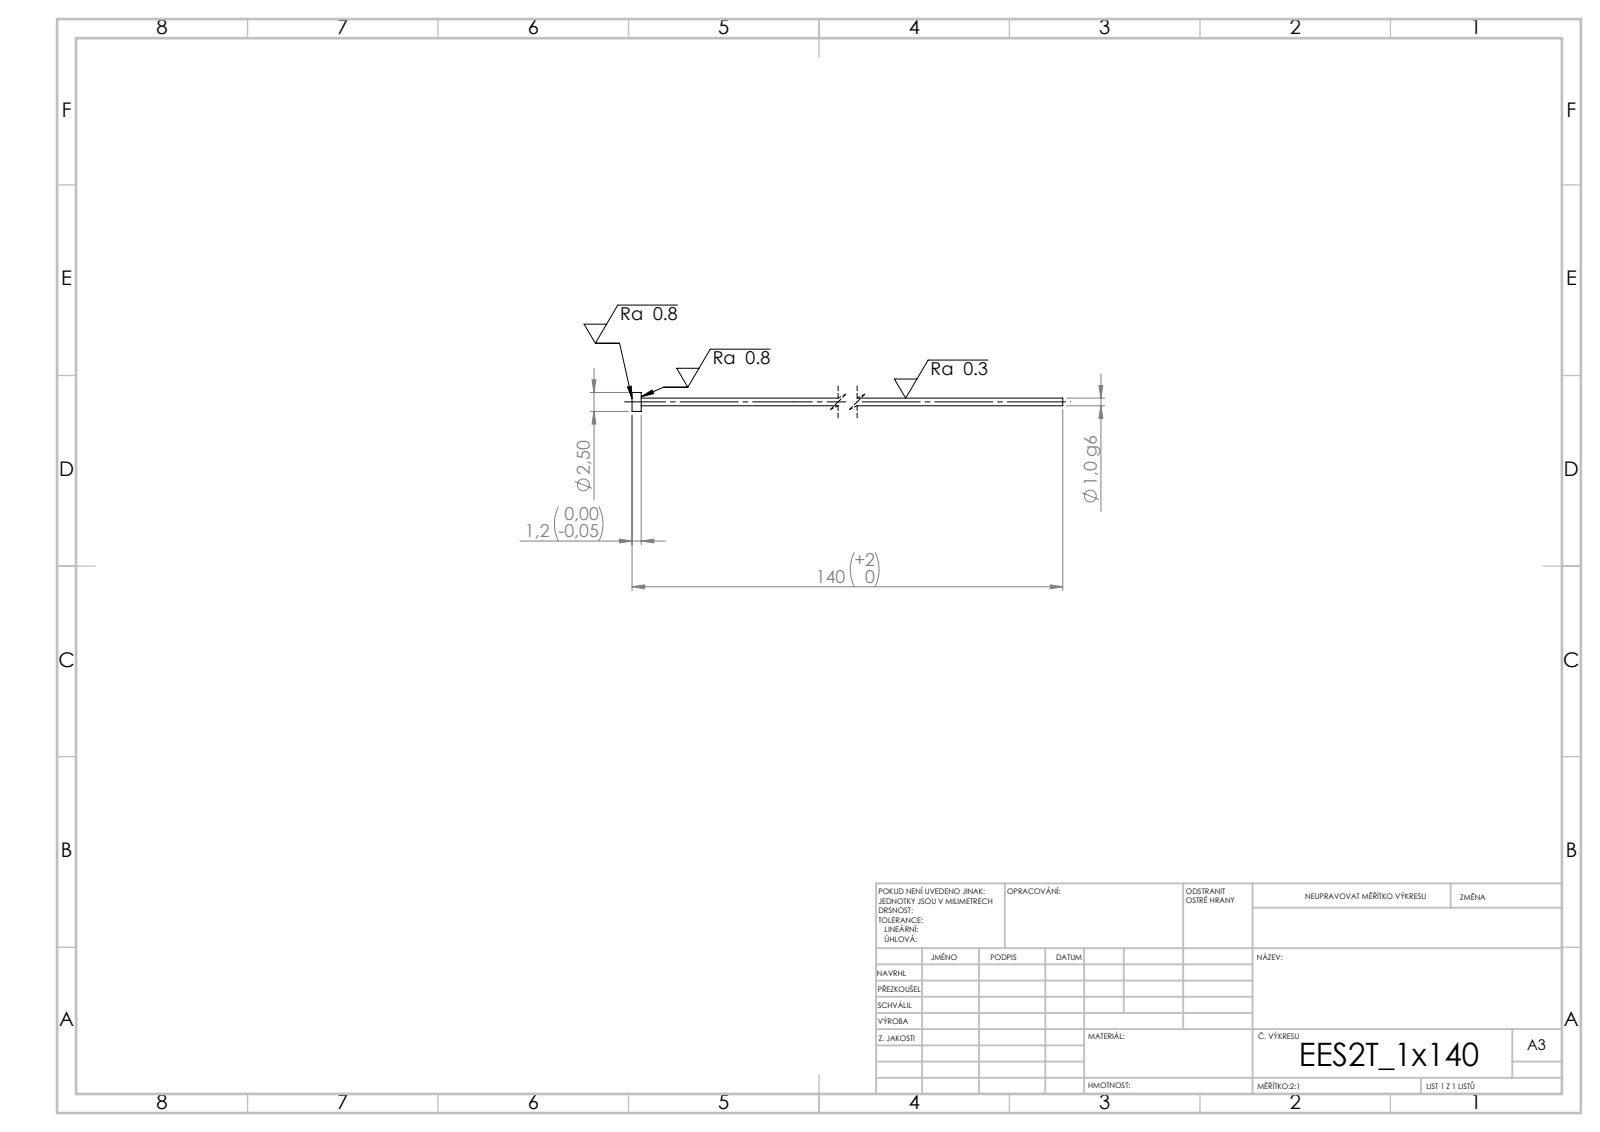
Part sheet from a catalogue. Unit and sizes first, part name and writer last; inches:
Units: inches
Overall size (bounding box): 5.512 × 0.098 × 0.098
Round bosses / shafts (diameter × count): ⌀0.098 ×1, ⌀0.039 ×1
Main face-to-face distances: 0.047, 5.512, 5.465
Volume: 0.007 in³ · Surface area: 0.705 in²
Bodies: 1 solid, 7 faces (3 planar, 4 cylindrical, 0 other)
STEP written by: SolidWorks 2019 (CONFIG_CONTROL_DESIGN)
